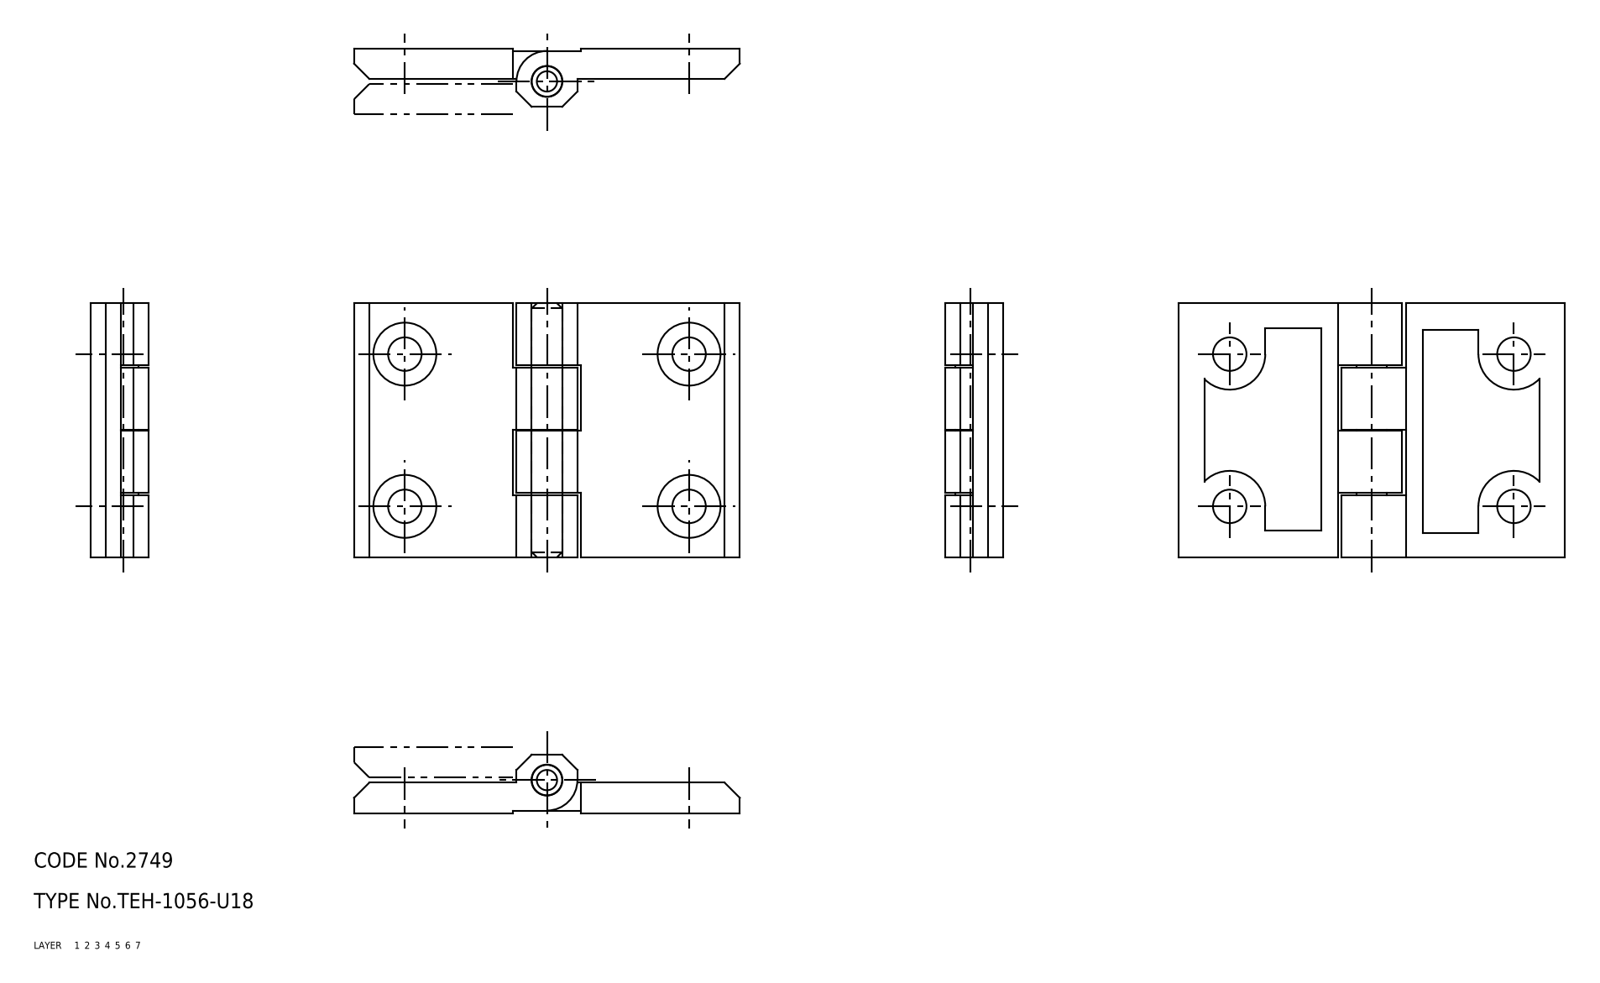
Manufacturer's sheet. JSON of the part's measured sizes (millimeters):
{"part_name": "shaft; hinge pieces_B; hinge pieces_A; TEH_1056_U18_2955_36", "step_written_by": "CADfix (AUTOMOTIVE_DESIGN)", "units": "millimeters", "bodies": {"solids": 3, "faces": 98, "planar": 0, "cylindrical": 0, "other": 98}, "overall_size": [76, 50, 11.5], "volume_mm3": 18904, "surface_area_mm2": 13016}
